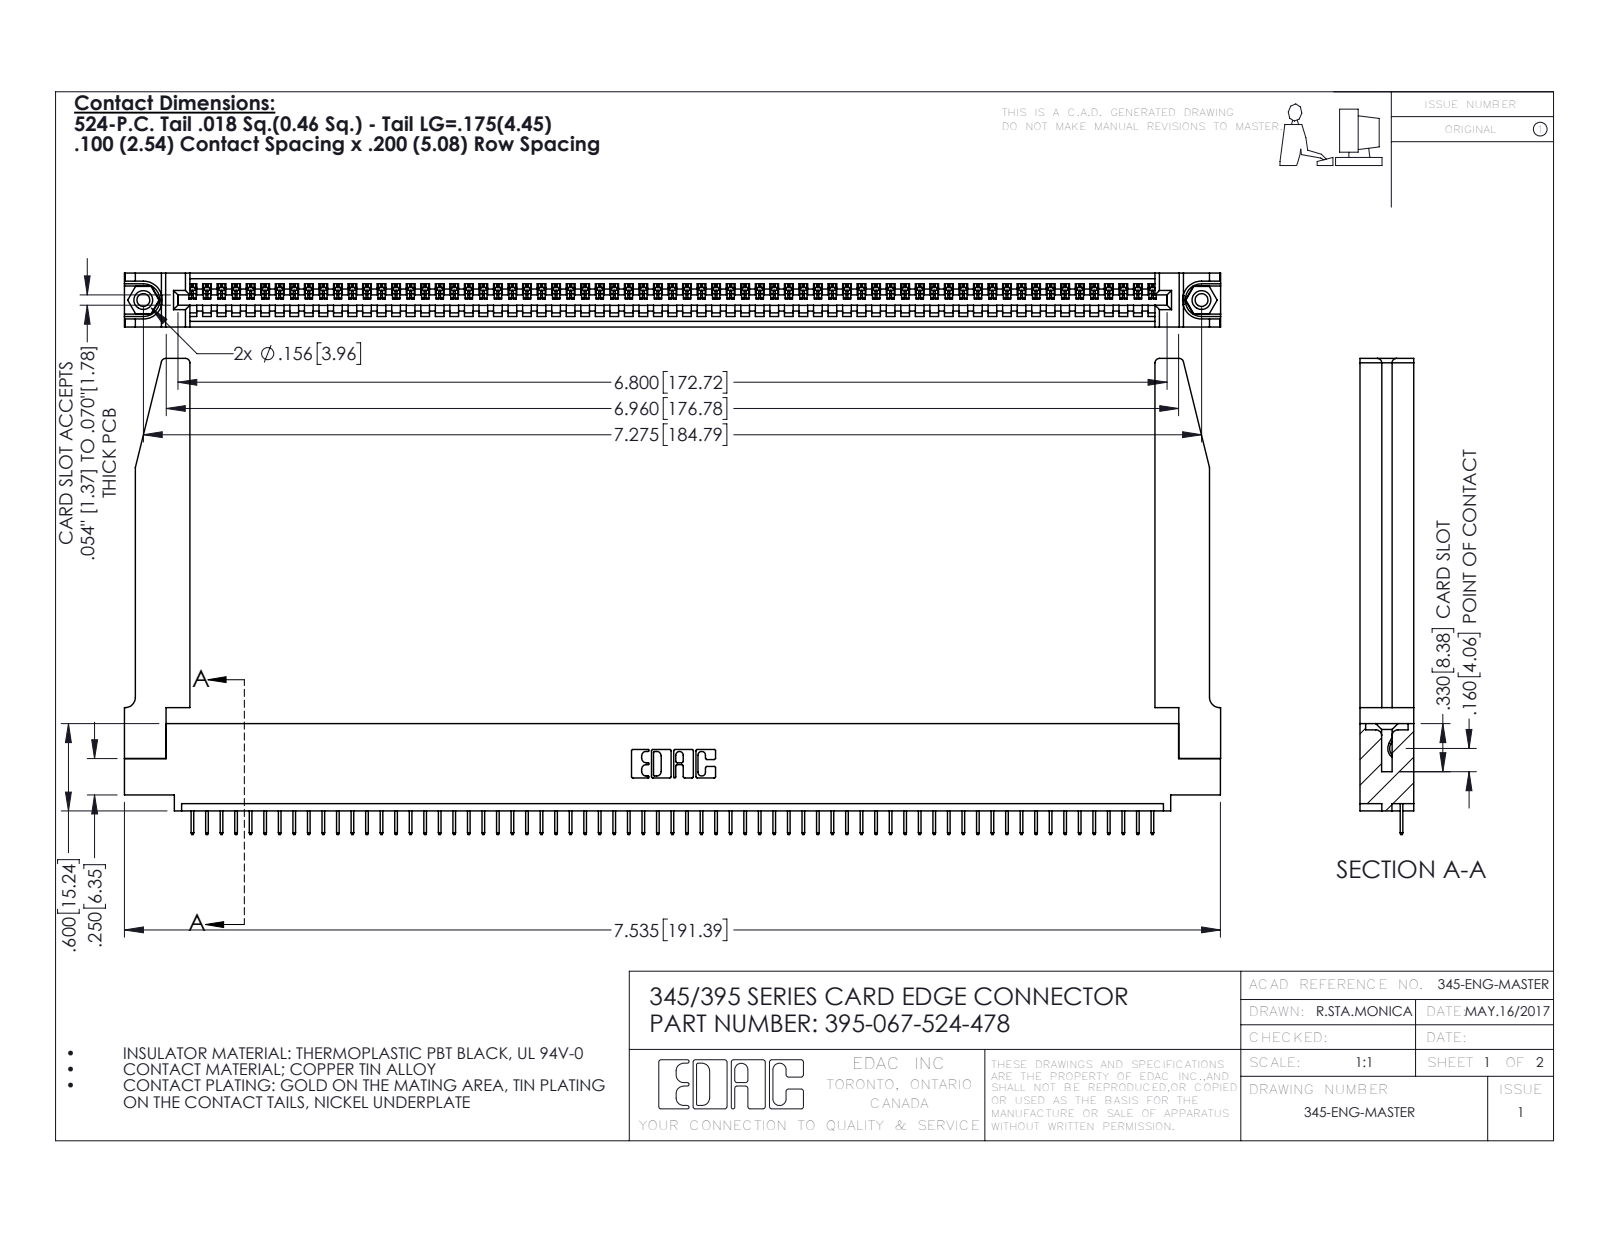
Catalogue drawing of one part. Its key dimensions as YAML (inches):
part_name: "345-250-001_345-250-001-102; 395-067-524-478; 345-292-001_345-293-124; 345 Part_0.110 Offset - 0.156 Dia-TH (+1 more)"
step_written_by: "SolidWorks 2016 (CONFIG_CONTROL_DESIGN)"
units: inches
bodies: {solids: 72, faces: 4518, planar: 3308, cylindrical: 1158, other: 52}
overall_size: [7.536, 3.272, 0.37]
volume: 1.576
surface_area: 47.13
round_holes:
  - {diameter: 0.089, count: 2}
  - {diameter: 0.125, count: 2}
  - {diameter: 0.156, count: 2}
  - {diameter: 0.064, count: 1}
round_bosses_or_shafts:
  - {diameter: 0.155, count: 2}
partial_cylinders:
  - {radius: 0.006, count: 134}
  - {radius: 0.01, count: 22}
  - {radius: 0.03, count: 8}
  - {radius: 0.007, count: 6}
  - {radius: 0.031, count: 6}
  - {radius: 0.026, count: 3}
  - {radius: 0.031, count: 2}
  - {radius: 0.04, count: 2}
face_to_face_distances: [0.37, 0.072, 0.298, 0.098, 0.272, 0.025, 0.2, 0.225, 0.072, 0.149]
hole_center_spacings: [0.27, 7.039, 7.275]
